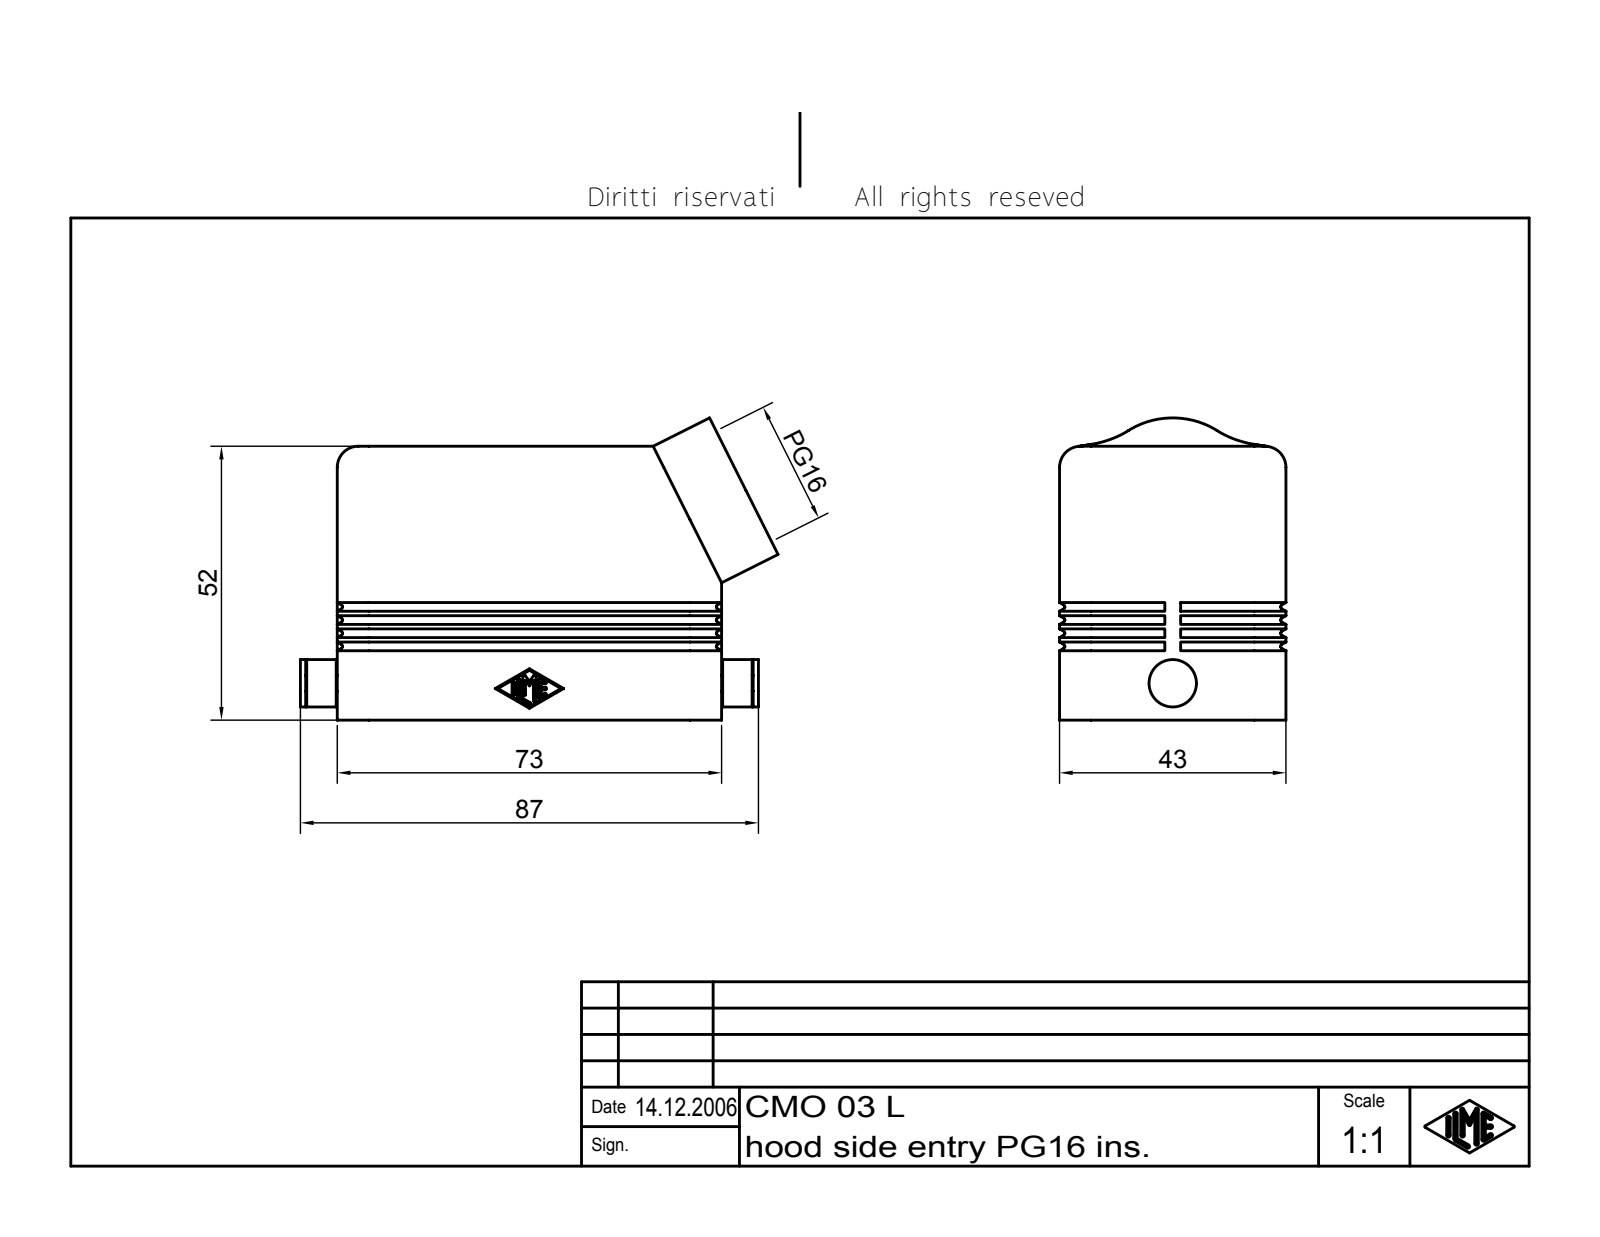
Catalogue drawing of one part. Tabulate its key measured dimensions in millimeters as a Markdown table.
| quantity | value |
| --- | --- |
| part name | CMO 03 L |
| STEP written by | Autodesk Inventor 7 (AUTOMOTIVE_DESIGN) |
| units | millimeters |
| bodies | 1 solid, 478 faces (120 planar, 192 cylindrical, 166 other) |
| overall size | 90.72 × 57.38 × 43 |
| volume | 52 633 mm³ |
| surface area | 30 016 mm² |
| round holes (diameter × count) | 14.66 × 1, 21.16 × 1 |
| round bosses / shafts (diameter × count) | 9 × 1, 3 × 1 |
| partial cylindrical surfaces (radius × count) | 0.4 × 32, 0.25 × 14, 1.5 × 4, 3 × 4, 6 × 4, 4 × 3, 5 × 2 |
| main face-to-face distances | 3, 40, 43, 37, 11.5, 8.5, 70, 61.5, 58.5, 31.5 |
